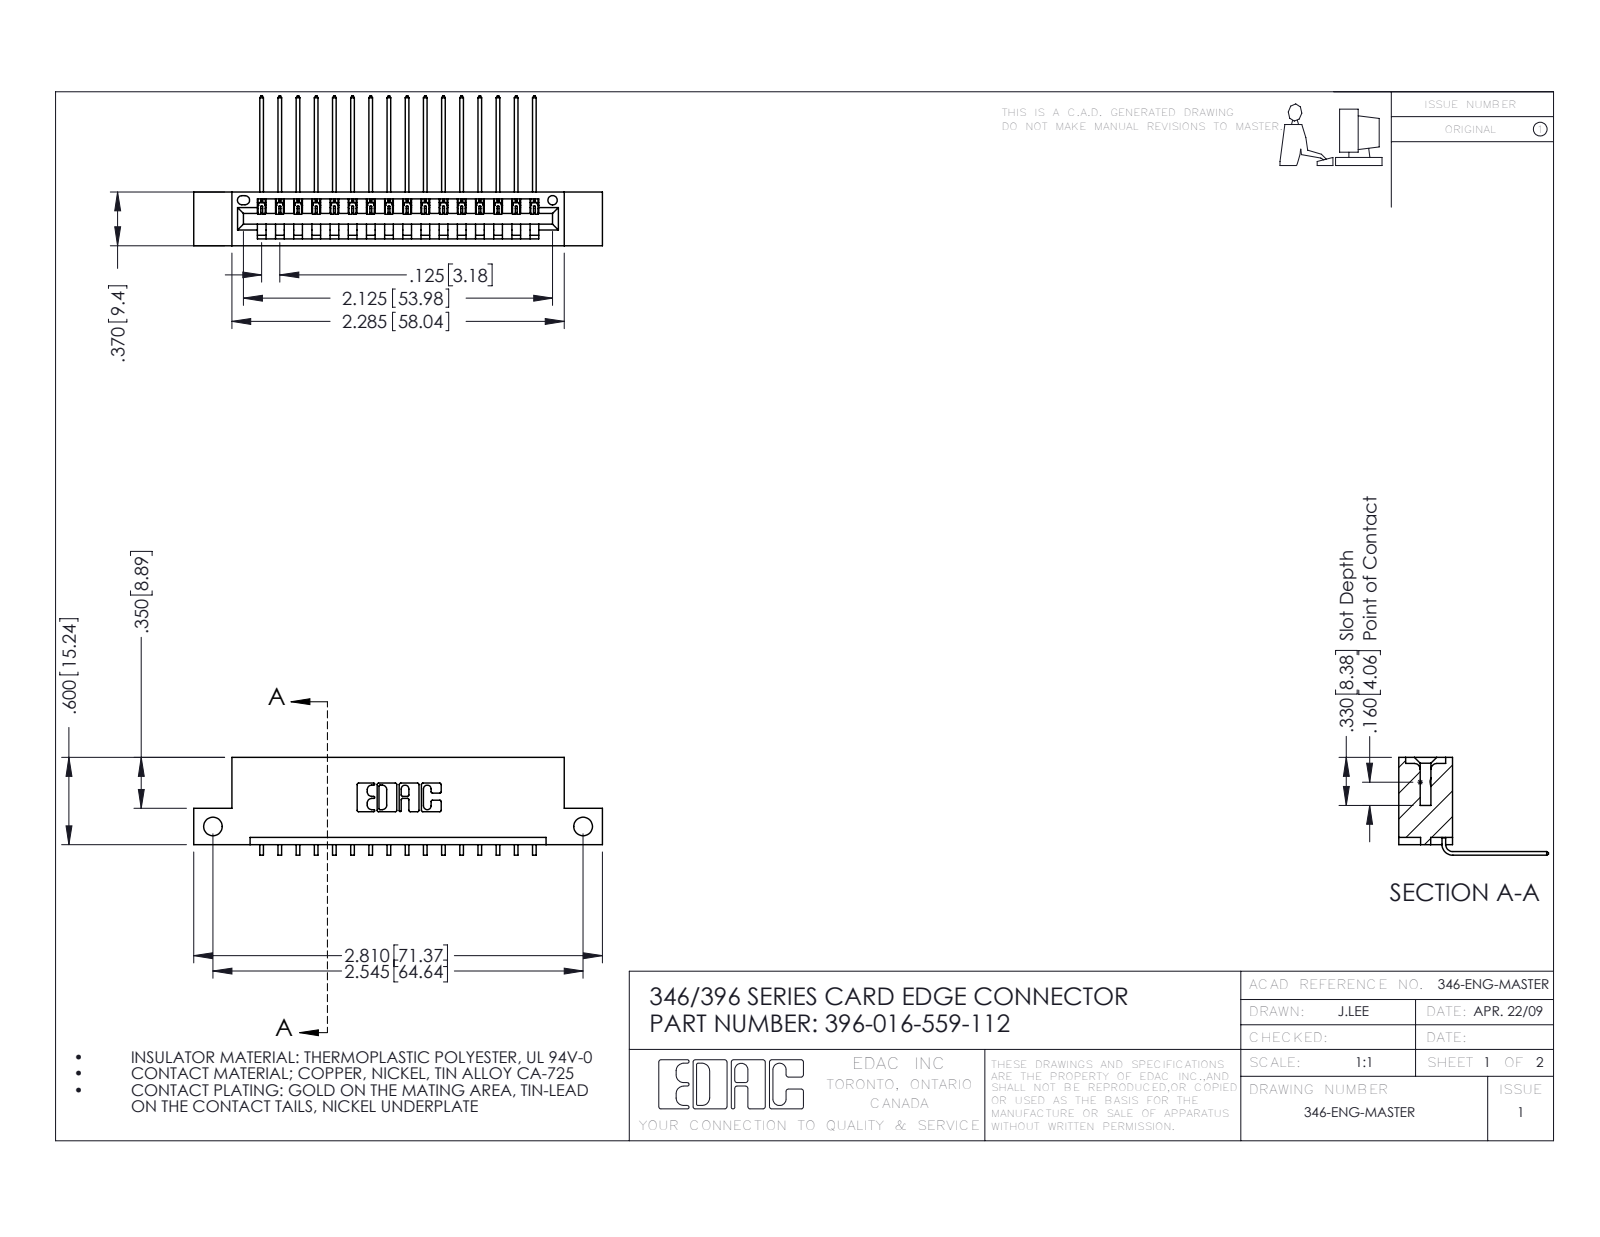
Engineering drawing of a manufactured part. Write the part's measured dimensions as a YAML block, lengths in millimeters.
part_name: "345-292-001_558 559 Tail - 1; 396-016-559-112; 346 Part_Flush Mounting Lugs - Side Mount"
step_written_by: "SolidWorks 2016 (CONFIG_CONTROL_DESIGN)"
units: millimeters
bodies: {solids: 17, faces: 1082, planar: 748, cylindrical: 334, other: 0}
overall_size: [71.4, 26.2, 17.1]
volume: 6620
surface_area: 8168
round_holes:
  - {diameter: 3.3, count: 2}
  - {diameter: 1.6, count: 1}
partial_cylinders:
  - {radius: 0.2, count: 32}
  - {radius: 0.3, count: 22}
  - {radius: 0.2, count: 6}
  - {radius: 0.8, count: 6}
  - {radius: 0.7, count: 3}
  - {radius: 0.8, count: 2}
  - {radius: 1, count: 2}
  - {radius: 0.4, count: 1}
face_to_face_distances: [1.2, 8.2, 6.4, 9.4, 1.8, 0.6, 7.6, 3.8, 5.6, 2.5]
hole_center_spacings: [64.6]
